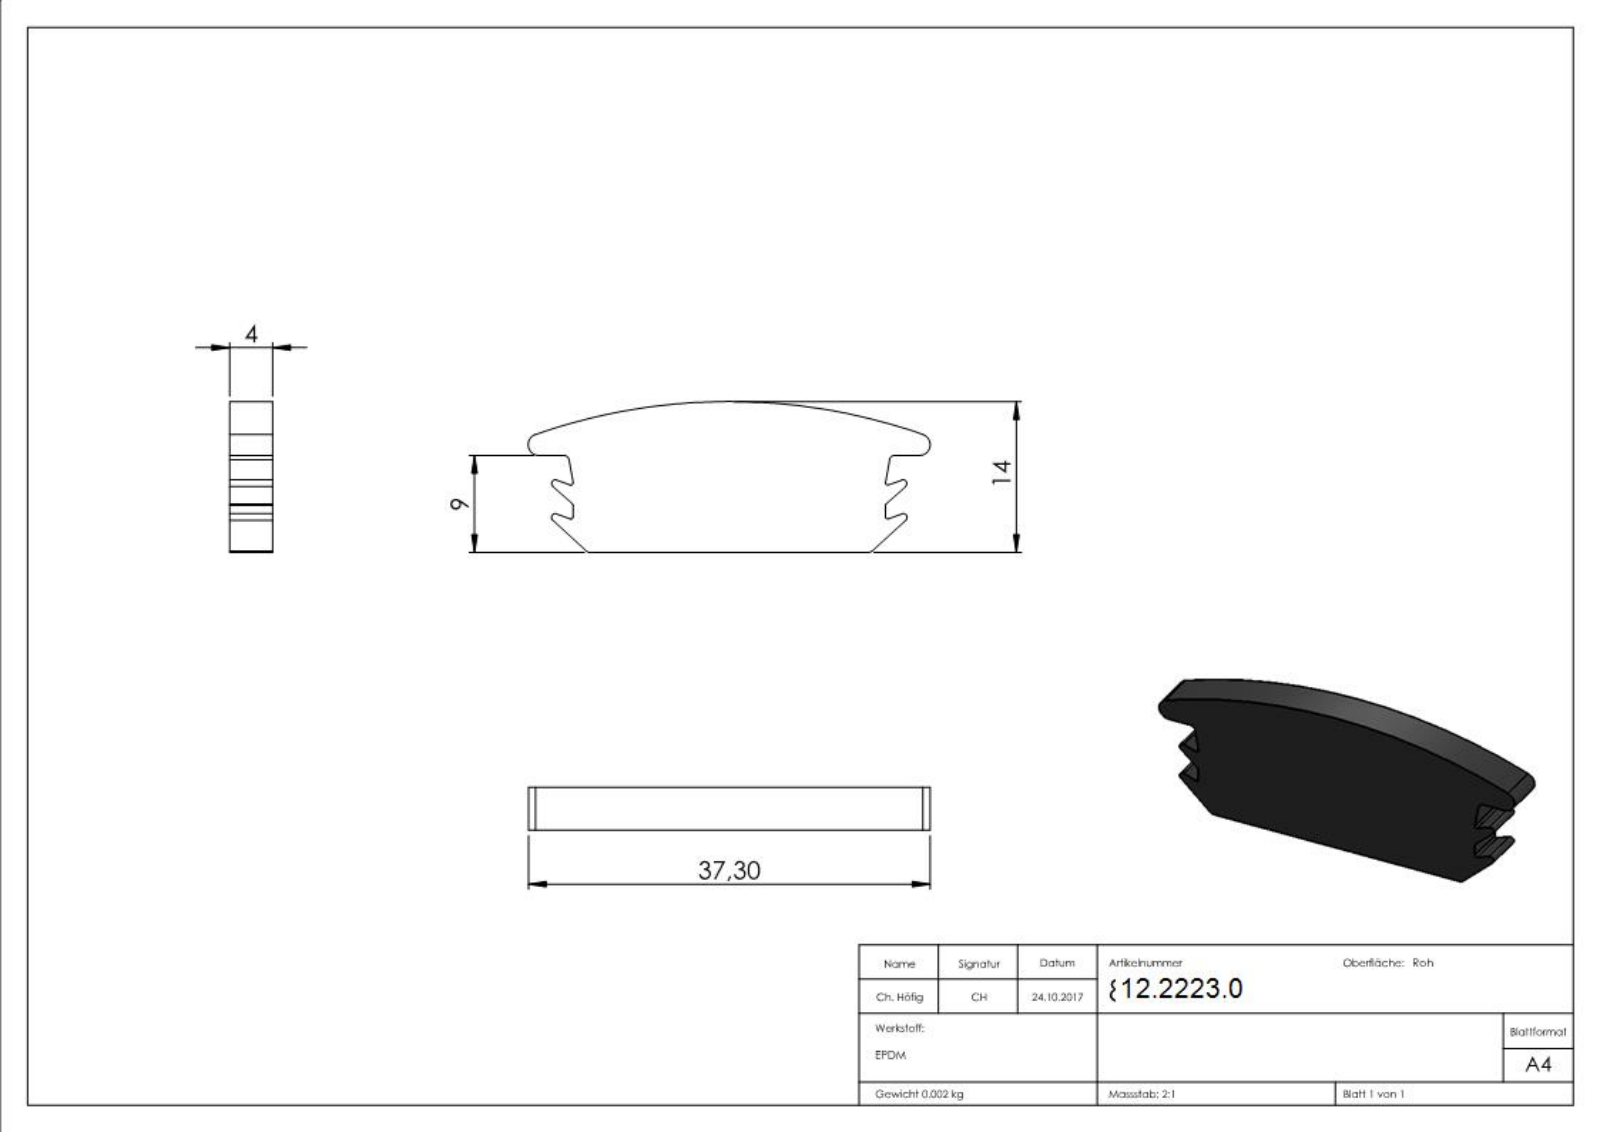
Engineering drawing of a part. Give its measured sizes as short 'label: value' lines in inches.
name: 80521-GU
written by: SolidWorks 2015 (CONFIG_CONTROL_DESIGN)
unit: in
bodies: 1 solid, 248 faces (125 planar, 19 cylindrical, 104 other)
size: 1.469 × 0.551 × 0.157
volume: 0.101 in³; area: 1.951 in²
rounds: 6× R0.008, 4× R0.014, 4× R0.02, 2× R0.039, 1× R2.143
face distances: 0.157, 0.354, 1.142, 0.35, 0.079, 0.048, 0.017, 0.051, 0.033, 0.45
